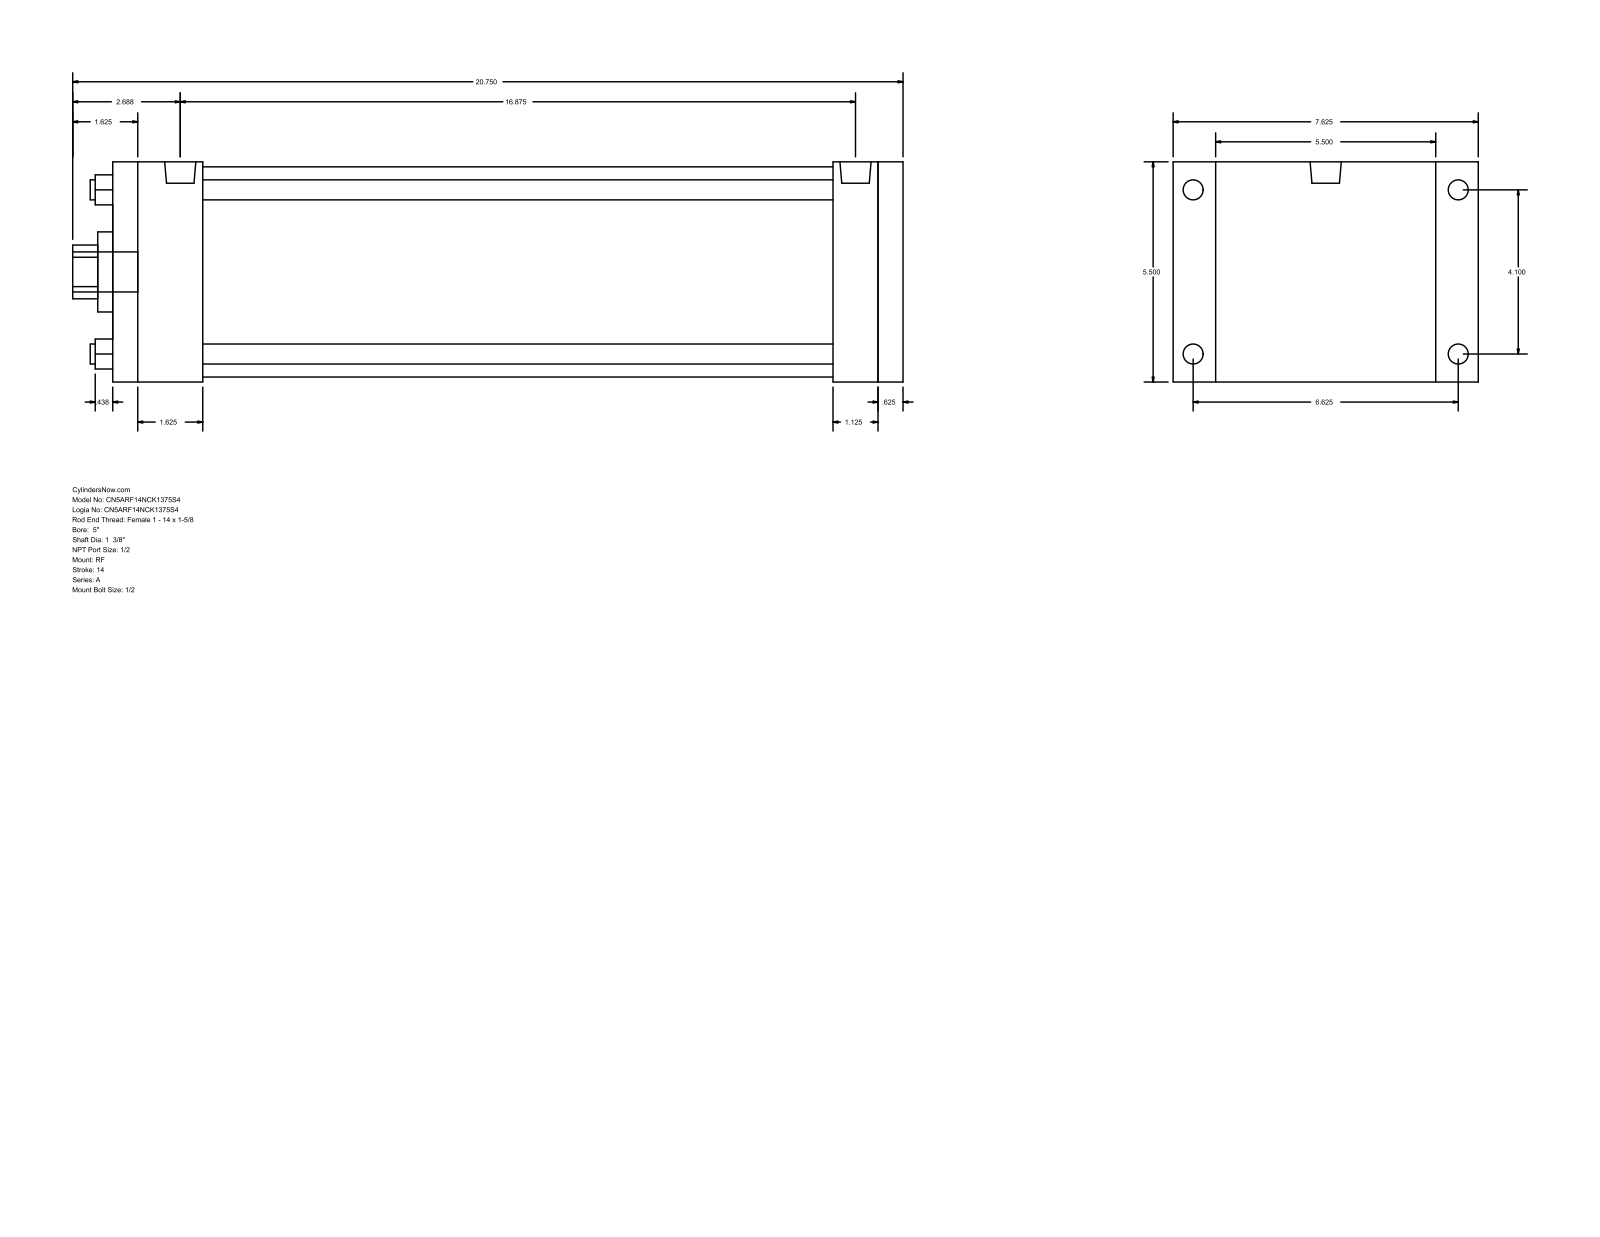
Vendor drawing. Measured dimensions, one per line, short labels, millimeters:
name: A_RF__0500_1.375
written by: GSSL Pune (CONFIG_CONTROL_DESIGN)
unit: mm
bodies: 0 solids, 92 faces (64 planar, 28 cylindrical, 0 other)
size: 527.05 × 193.68 × 139.7
holes: 4× ⌀12.7, 1× ⌀34.92, 1× ⌀50.8, 1× ⌀133.35
bosses: 4× ⌀12.7, 4× ⌀8.73, 2× ⌀19.77, 1× ⌀25.4
rounds: 1× R17.06
face distances: 139.7, 501.65, 15.87, 485.78, 28.58, 57.15, 428.63, 444.5, 457.2, 400.05
hole spacings: 73.64, 104.14, 147.28
